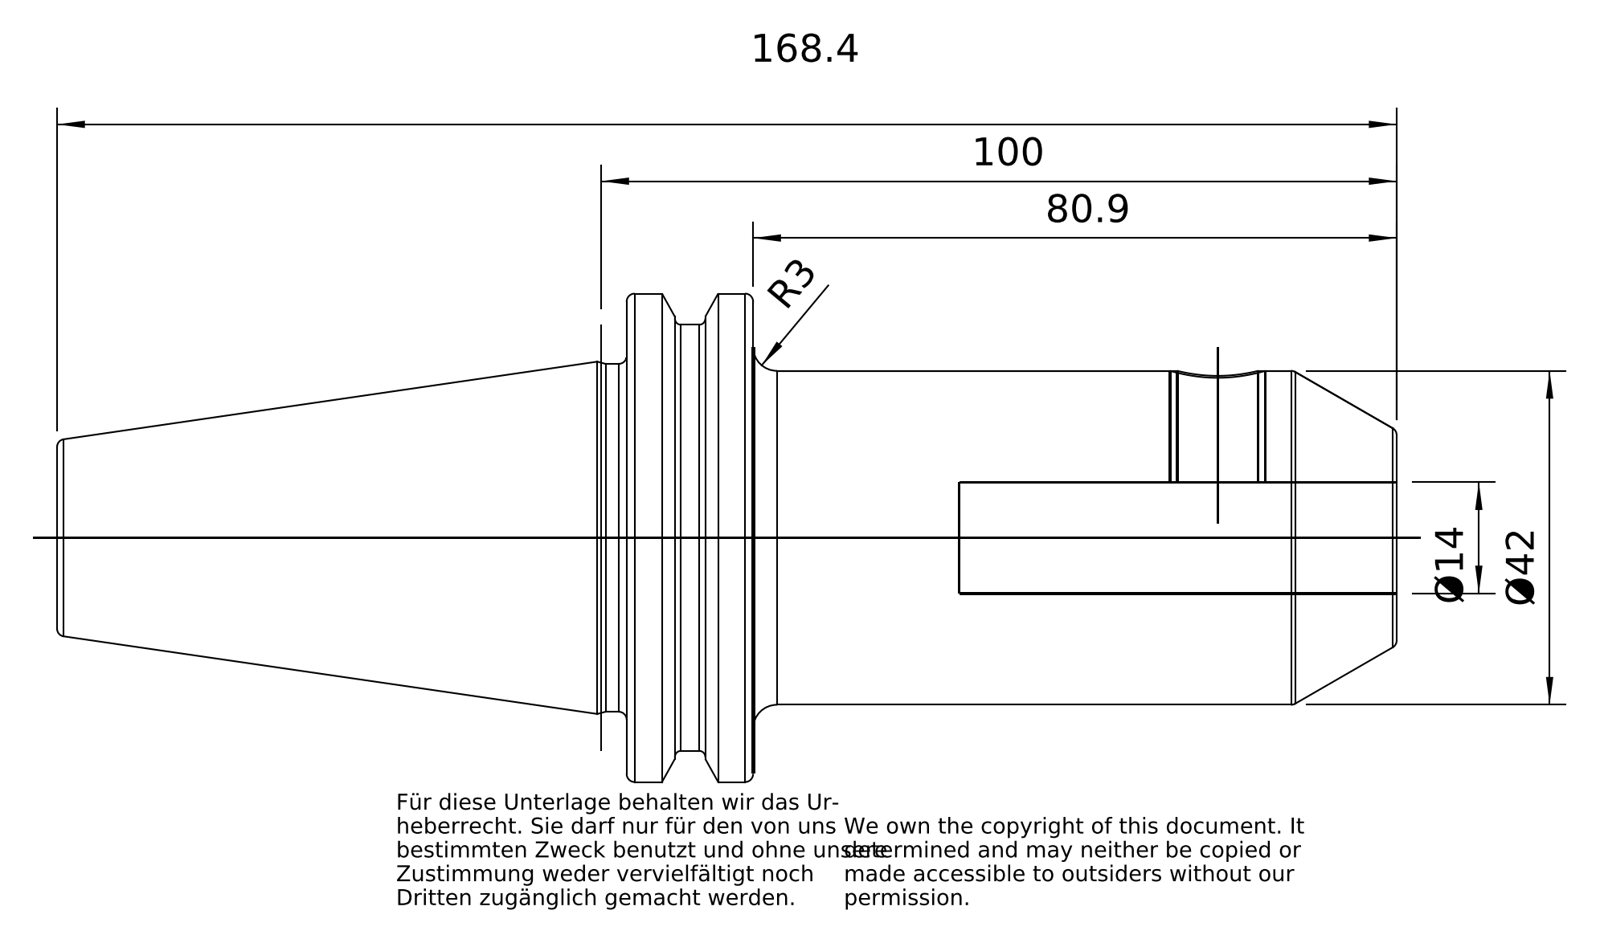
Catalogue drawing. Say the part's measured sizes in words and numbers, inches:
The part is named "40-301-14". Its 3-D file was written by "PRO/ENGINEER BY PARAMETRIC TECHNOLOGY CORPORATION, 2010430 (CONFIG_CONTROL_DESIGN)". It is 1 solid with 99 faces: 21 planar, 28 cylindrical and 50 other. Overall it measures 6.624 by 2.501 by 2.418 inches. Its volume is 12.38 cubic inches and its surface area 50.94 square inches. Round holes: 1 of diameter 0.402, 1 of diameter 0.472, 1 of diameter 0.545, 1 of diameter 0.551, 1 of diameter 0.67, 1 of diameter 0.689. Round bosses or shafts: 1 of diameter 1.722, 1 of diameter 1.654, 1 of diameter 0.63. Partial cylindrical surfaces (rounded edges, fillets, slot ends): 1 of radius 0.053, 1 of radius 1.102, 1 of radius 1.25. The main face-to-face distances are 0.624, 3.811, 3.187, 1.866, 0.638, 1.642, 1.018, 2.169, 2.813, 3.437.
